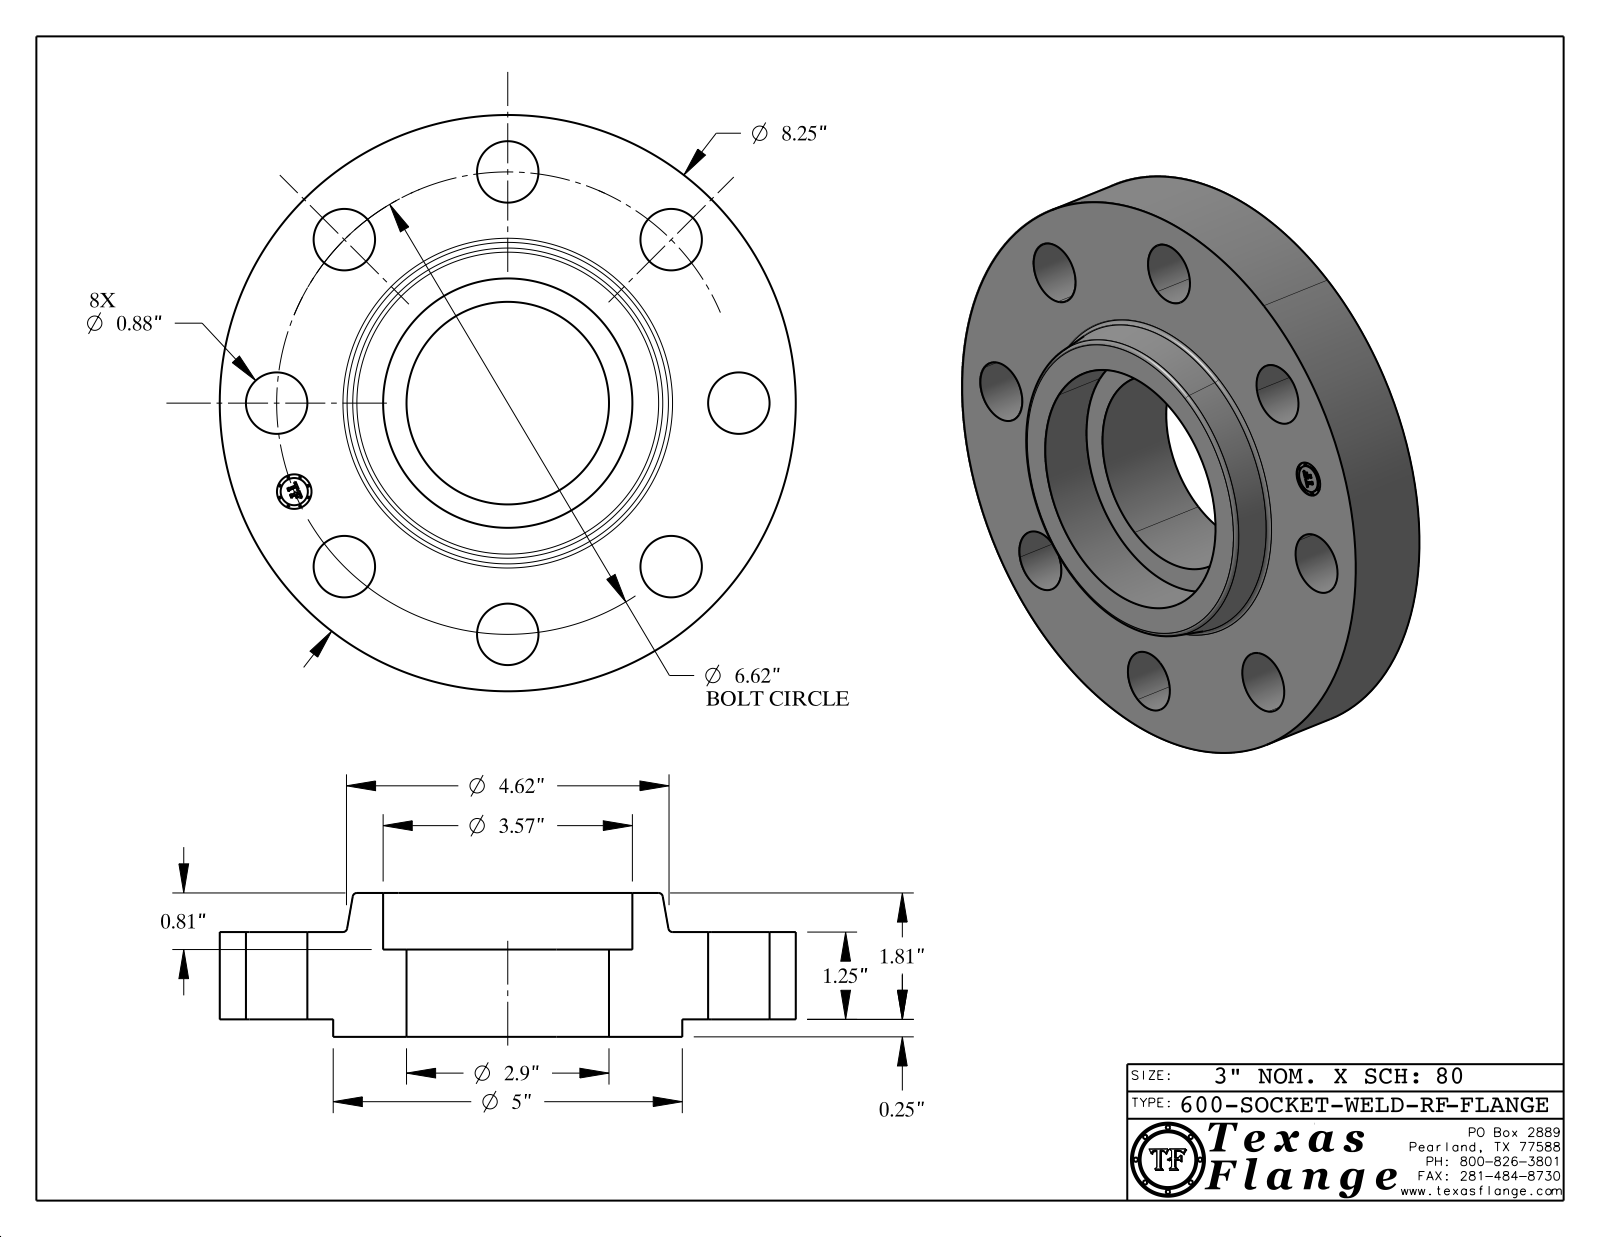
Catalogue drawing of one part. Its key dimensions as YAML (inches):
part_name: "600-SOCKET-WELD-RF"
step_written_by: "CATIA V5 STEP AP214 (AUTOMOTIVE_DESIGN)"
units: inches
bodies: {solids: 1, faces: 420, planar: 370, cylindrical: 44, other: 6}
overall_size: [8.25, 8.25, 2.06]
volume: 58.27
surface_area: 174.7
round_holes:
  - {diameter: 0.88, count: 8}
  - {diameter: 0.495, count: 1}
  - {diameter: 2.9, count: 1}
  - {diameter: 3.57, count: 1}
round_bosses_or_shafts:
  - {diameter: 0.03, count: 8}
  - {diameter: 8.25, count: 1}
  - {diameter: 5, count: 1}
  - {diameter: 0.39, count: 1}
face_to_face_distances: [1.25, 0.25, 1.5, 2.06, 1.81, 0.56, 1, 0.81, 0.015, 1.485]
hole_center_spacings: [3.31, 2.533, 6.116, 4.681, 4.681, 1.291, 3.678, 6.493]
